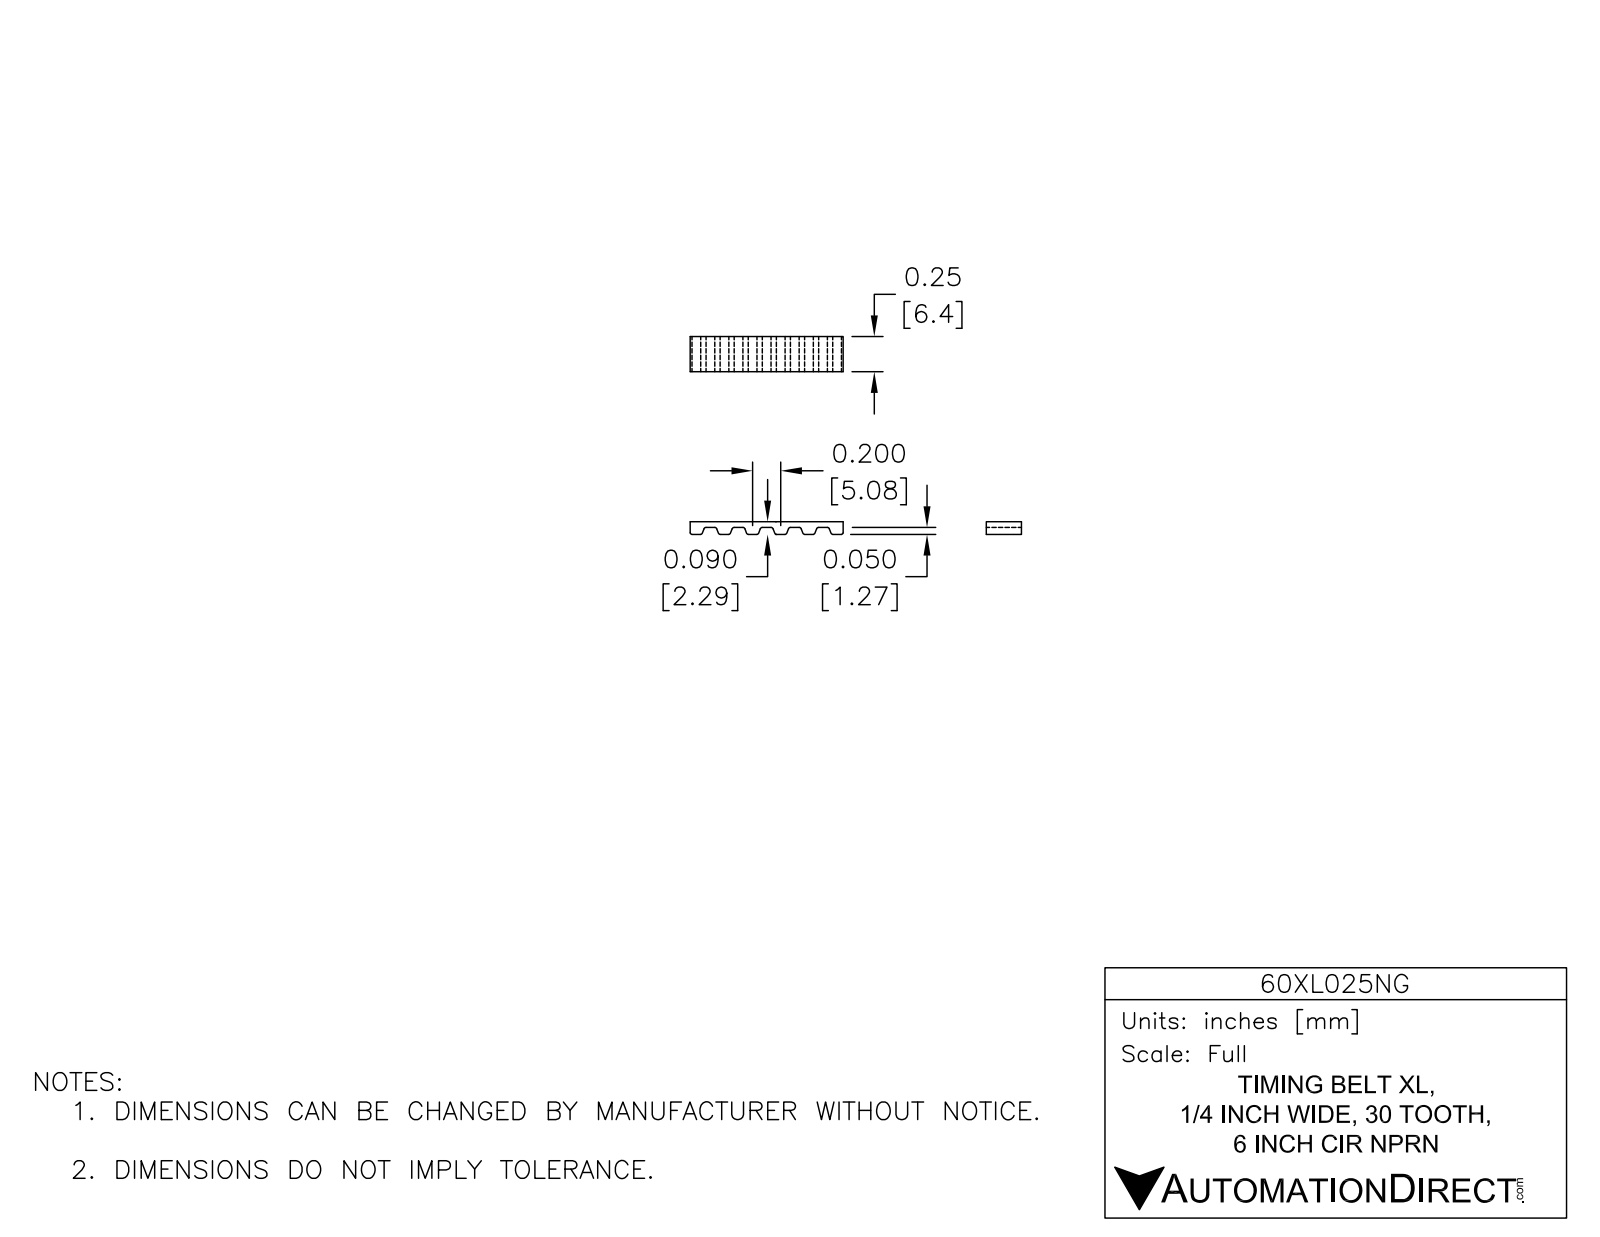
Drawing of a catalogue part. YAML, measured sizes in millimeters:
part_name: "60XL025NG"
step_written_by: "SolidWorks 2014 (AUTOMOTIVE_DESIGN)"
units: millimeters
bodies: {solids: 1, faces: 258, planar: 106, cylindrical: 152, other: 0}
overall_size: [59.1, 30, 6.4]
volume: 1300
surface_area: 2576
partial_cylinders:
  - {radius: 0.4, count: 120}
  - {radius: 14, count: 2}
  - {radius: 15, count: 2}
face_to_face_distances: [6.4, 30, 1, 29, 4.4, 28, 8.8, 9.9, 13.2, 14.4]
